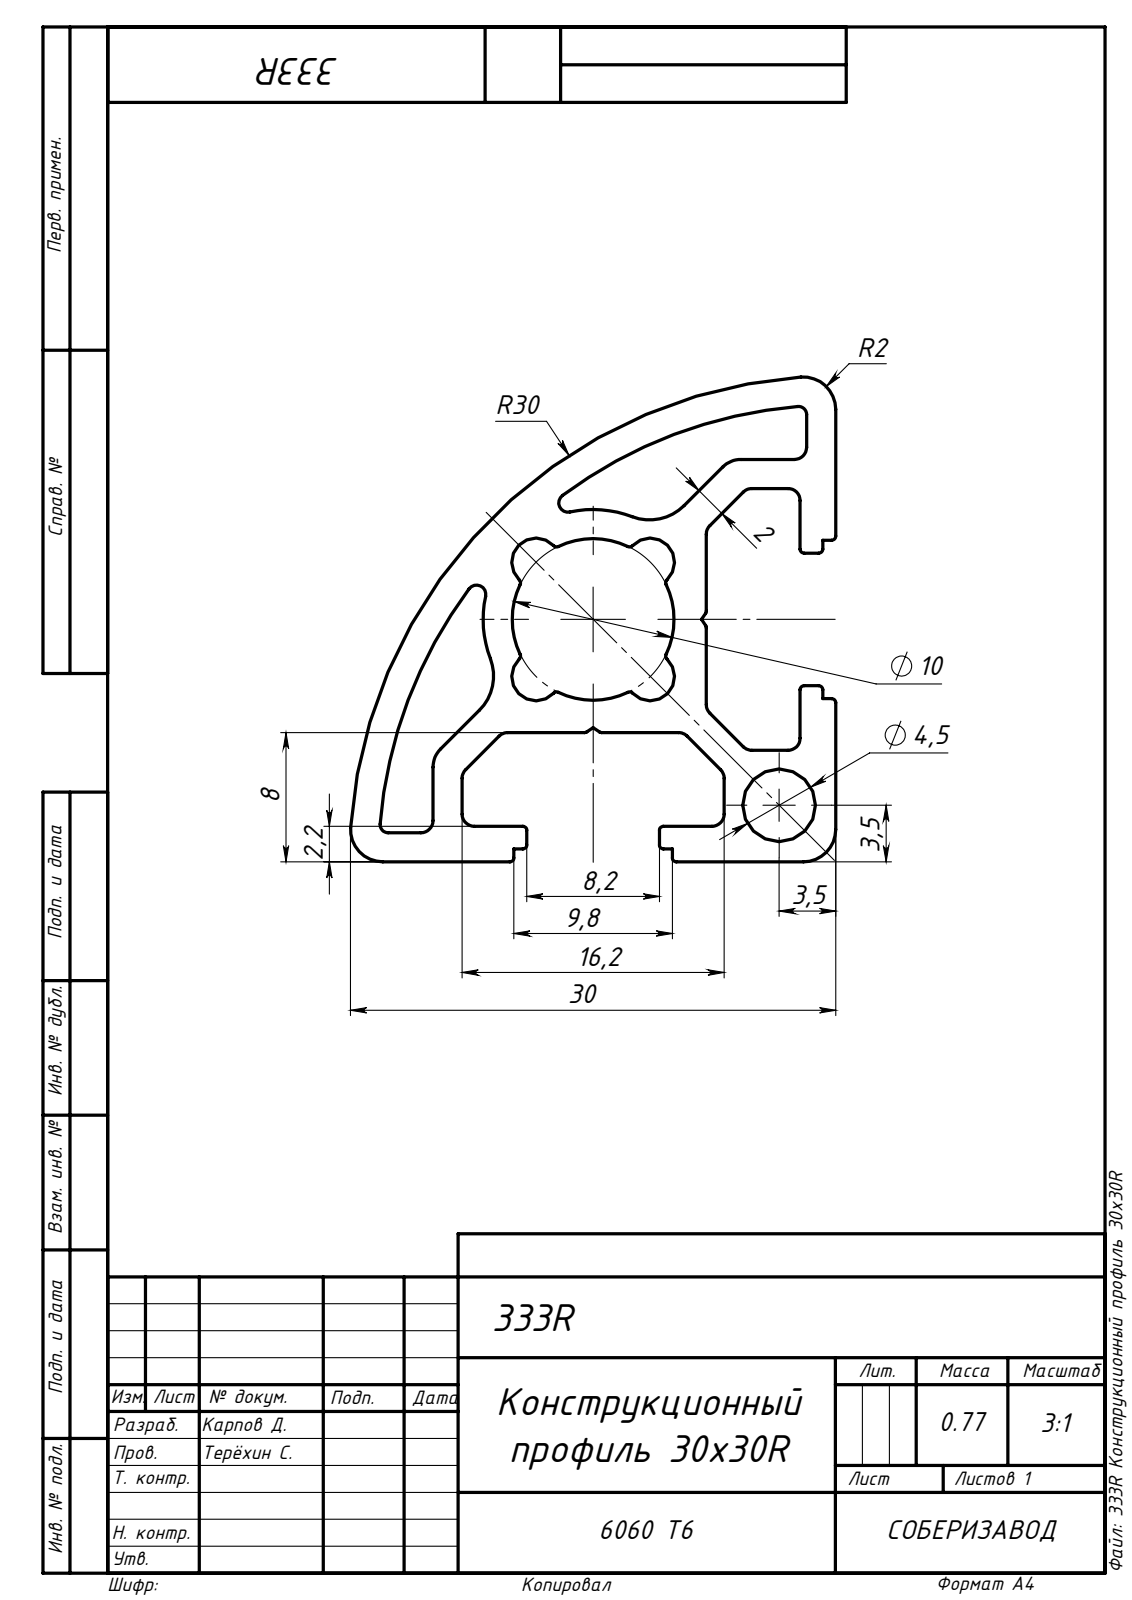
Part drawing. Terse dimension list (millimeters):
written by: SolidWorks 2014 (AUTOMOTIVE_DESIGN)
unit: mm
bodies: 1 solid, 113 faces (44 planar, 69 cylindrical, 0 other)
size: 1000 × 30 × 30
volume: 284 021 mm³; area: 287 872 mm²
holes: 1× ⌀4.5
rounds: 24× R0.25, 14× R0.75, 4× R1.5, 3× R2, 2× R0.5, 2× R0.57, 2× R1.6, 2× R3
face distances: 8, 5.8, 2.2, 2, 1.8, 23.1, 16.9, 22.7, 24.9, 15.1
